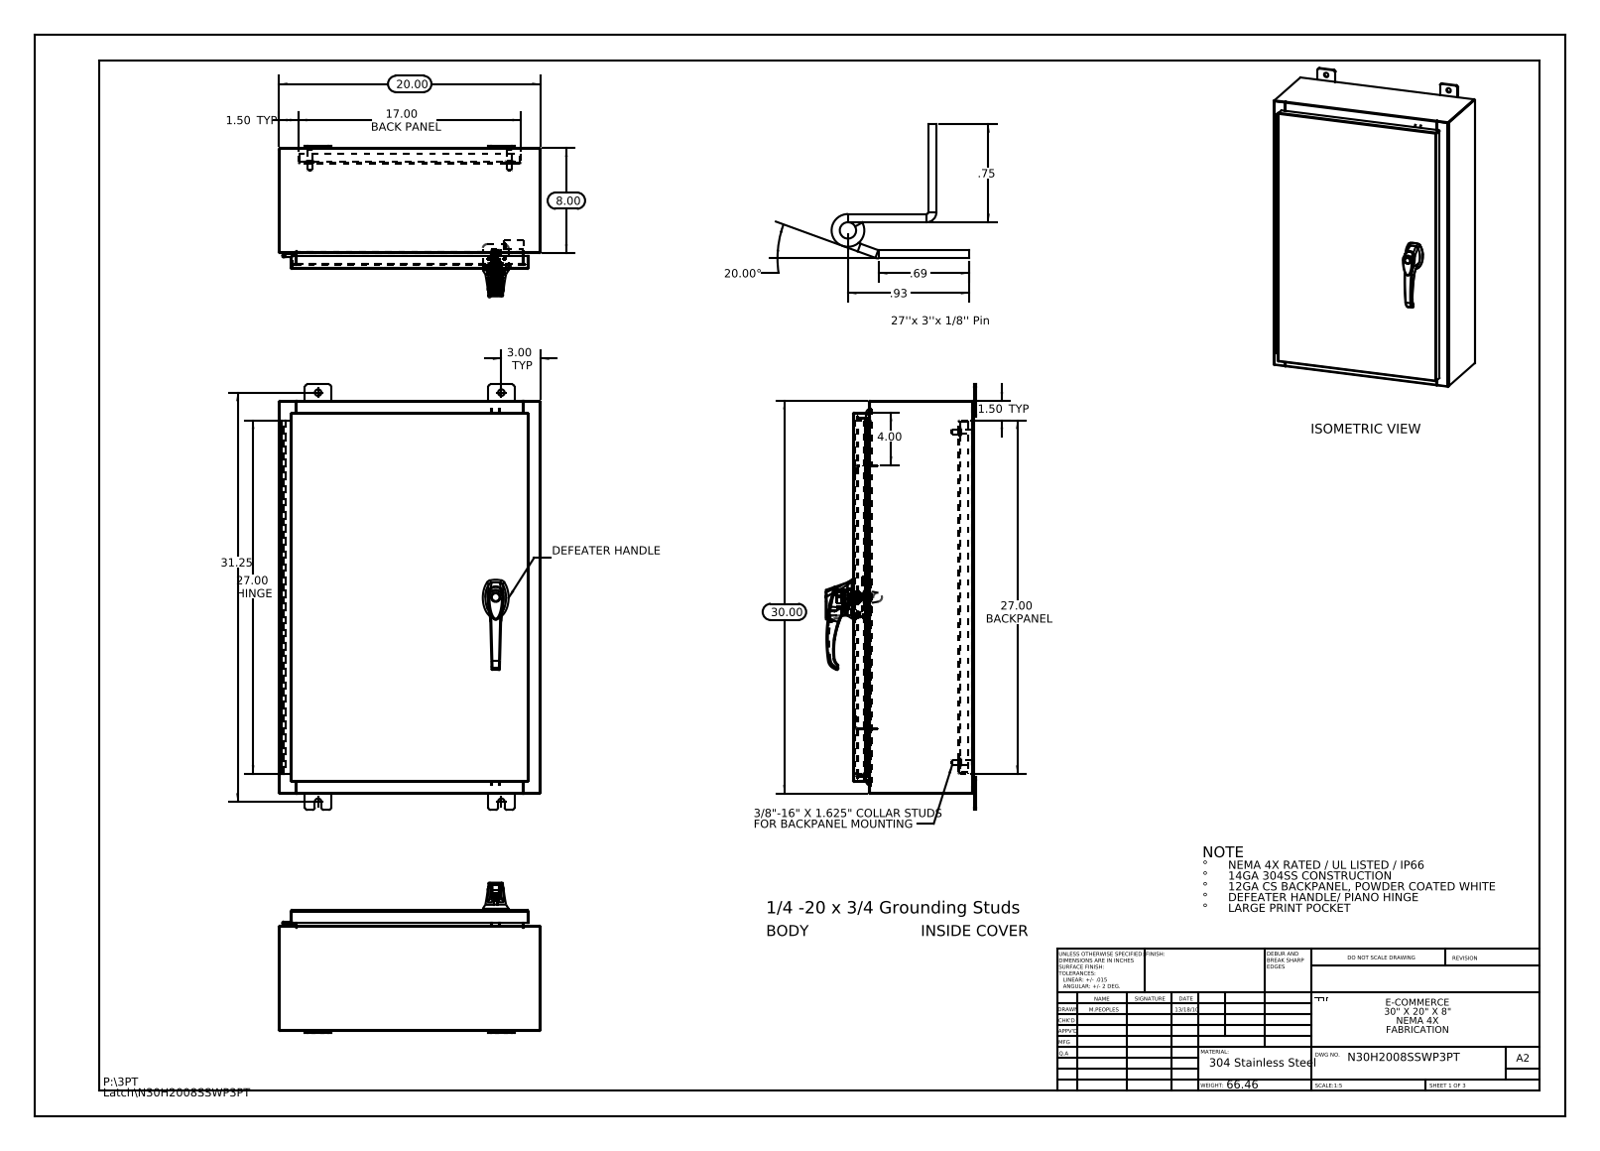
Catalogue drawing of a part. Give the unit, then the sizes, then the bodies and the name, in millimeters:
Units: millimetres
Overall size (bounding box): 825.5 × 508 × 292
Round holes (diameter × count): ⌀12.7 ×8, ⌀6.4 ×4, ⌀3.5 ×3, ⌀4.1 ×3, ⌀2 ×2, ⌀5.2 ×2, ⌀8 ×2, ⌀11.1 ×2, ⌀3.2 ×1, ⌀3.2 ×1, ⌀5 ×1, ⌀7 ×1
Round bosses / shafts (diameter × count): ⌀15.9 ×4, ⌀9.5 ×4, ⌀8.4 ×4, ⌀30 ×1, ⌀19 ×1, ⌀17.3 ×1, ⌀16.8 ×1, ⌀16.2 ×1
Partial cylindrical surfaces — rounded edges, fillets, slot ends (radius × count): R3 ×37, R0.2 ×33, R0.3 ×24, R4.8 ×24, R2.2 ×18, R1 ×15, R0.7 ×12, R0.2 ×6
Main face-to-face distances: 1.9, 231.8, 2.6, 229.9, 233.7, 506.1, 25.4, 27.3, 204.5, 206.4
Hole centre spacings: 212.6, 384.6, 7.5, 15.9, 21.4, 31.8, 33.4, 39.6
Volume: 3 872 000 mm³ · Surface area: 3 768 000 mm²
Bodies: 31 solids, 2576 faces (953 planar, 969 cylindrical, 654 other)
Part name (STEP PRODUCT): N30H2008SSWP3PT Mounting Studs; 00005090; 022151; g26103103_26163303 (+8 more)
STEP written by: SolidWorks 2013 (CONFIG_CONTROL_DESIGN)
